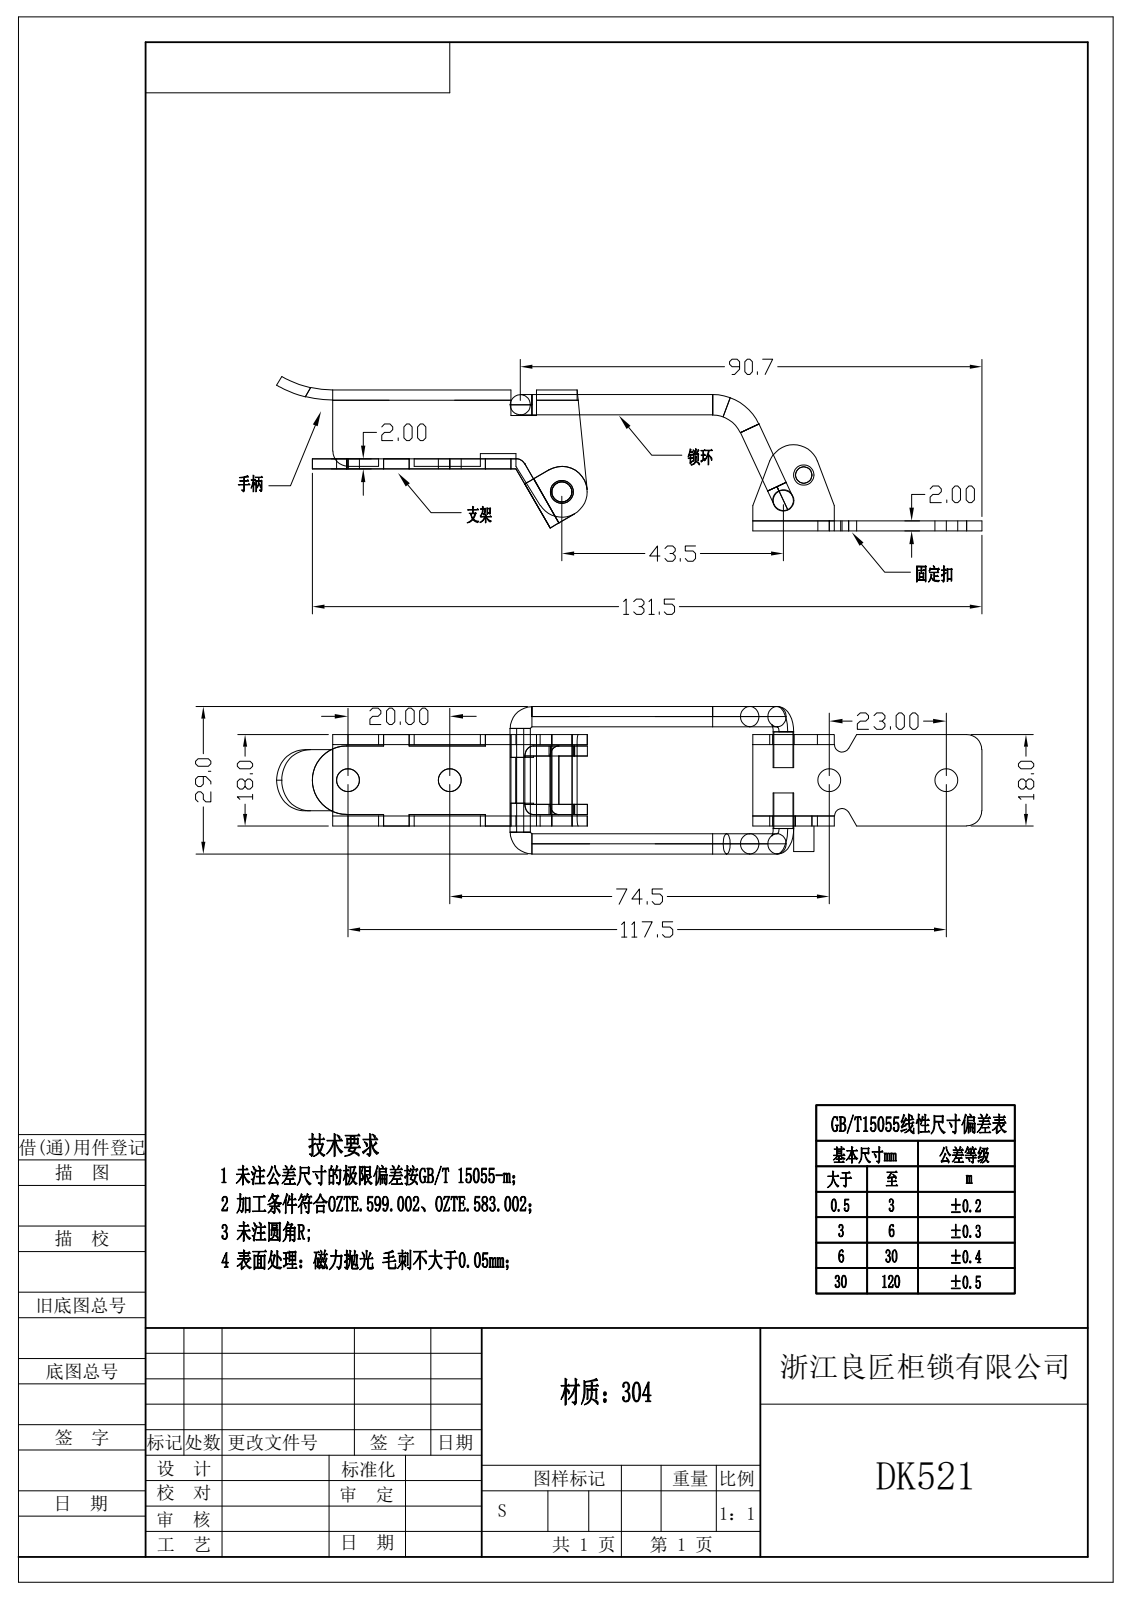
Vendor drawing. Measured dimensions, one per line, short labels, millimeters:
written by: Rhino 8.5 (CONFIG_CONTROL_DESIGN)
unit: mm
bodies: 6 solids, 217 faces (117 planar, 79 cylindrical, 21 other)
size: 138.71 × 30.16 × 29
volume: 10 629 mm³; area: 12 308 mm²
holes: 6× ⌀4.5, 1× ⌀3.3, 1× ⌀4
bosses: 7× ⌀4, 1× ⌀6
rounds: 4× R0.32, 4× R1.5, 3× R3, 2× R0.5, 2× R1.72, 2× R2, 2× R5, 1× R0.2
face distances: 2, 16, 14, 12, 18, 1.7, 13.5, 11.5, 10, 27.48
hole spacings: 6.4, 19.5, 23, 44.75, 48.85, 75.74, 95.24, 98.73
